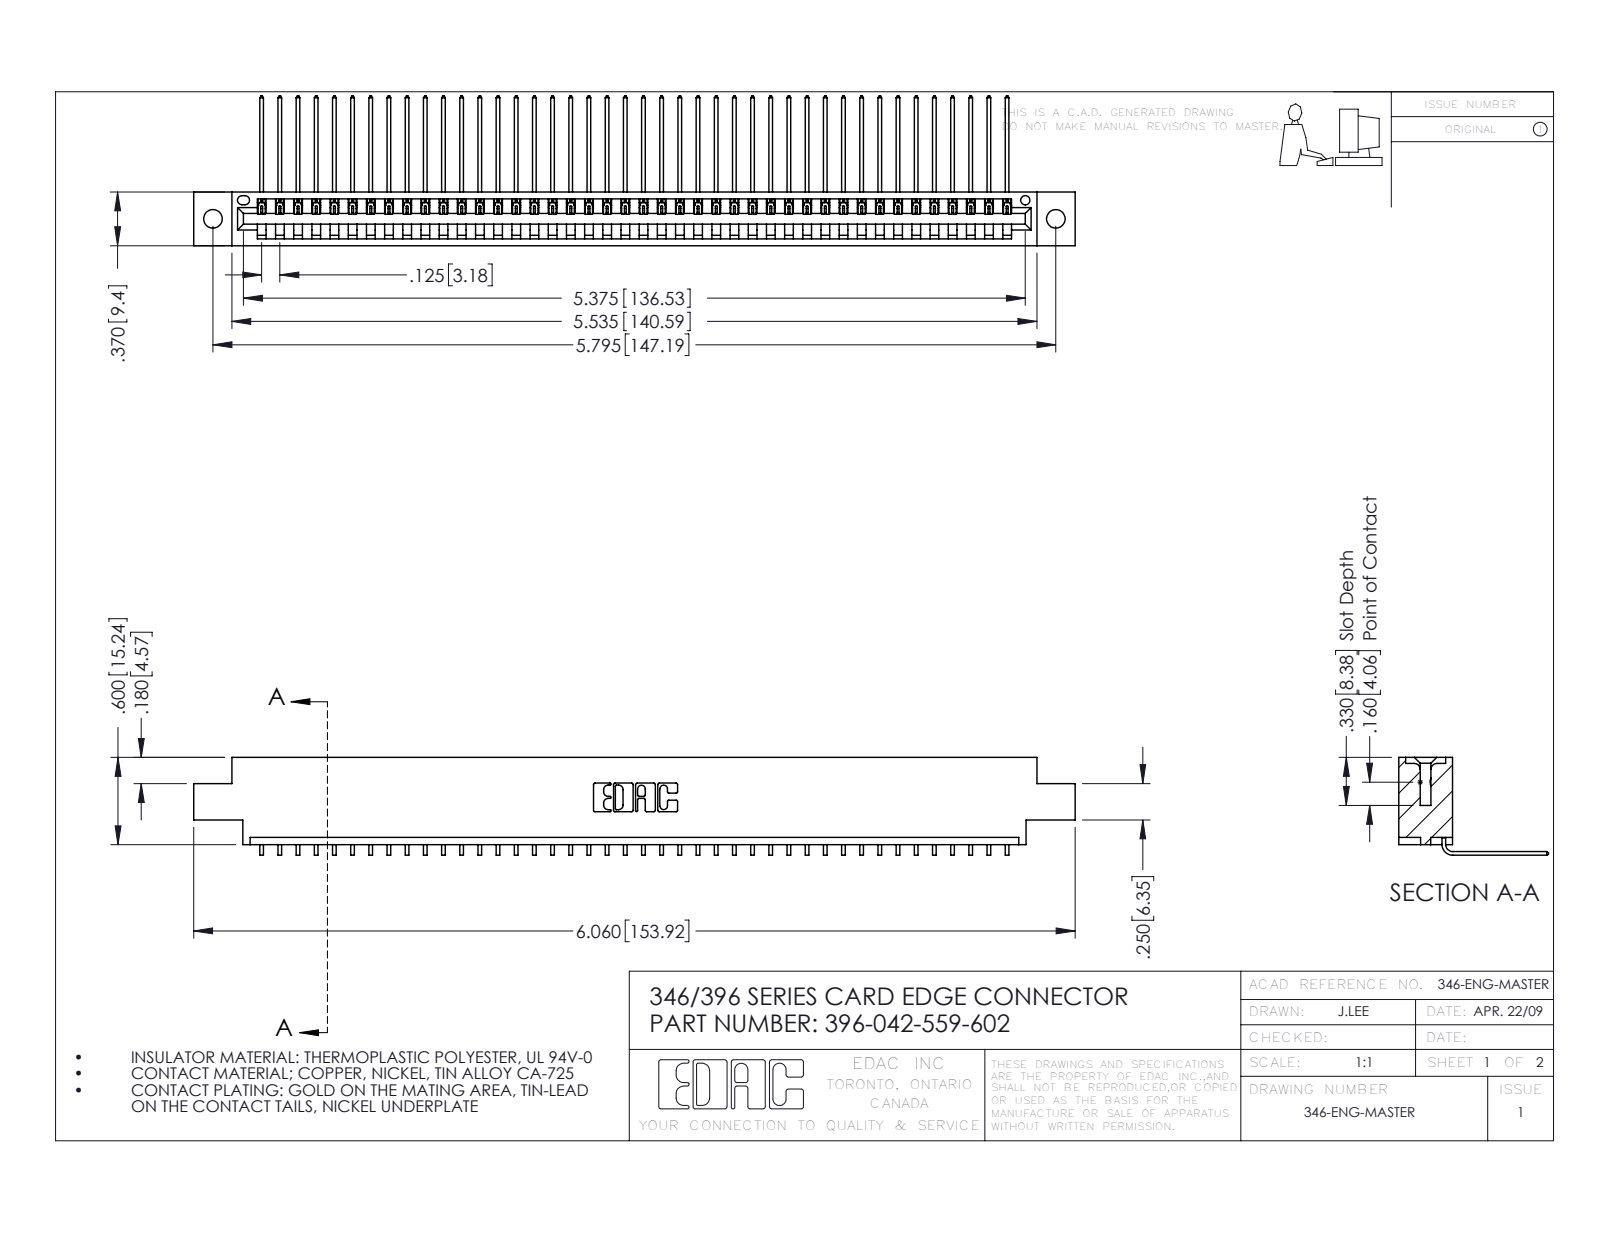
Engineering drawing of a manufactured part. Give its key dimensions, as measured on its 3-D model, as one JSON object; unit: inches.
{"part_name": "345-292-001_558 559 Tail - 1; 346 Part_0.170 Offset - 0.128 Dia; 396-042-559-602", "step_written_by": "SolidWorks 2016 (CONFIG_CONTROL_DESIGN)", "units": "inches", "bodies": {"solids": 43, "faces": 2646, "planar": 1844, "cylindrical": 802, "other": 0}, "overall_size": [6.06, 1.03, 0.673], "volume_in3": 0.896, "surface_area_in2": 29.57, "round_holes": [[0.128, 2], [0.064, 1]], "partial_cylinders_radius": [[0.006, 84], [0.01, 22], [0.007, 6], [0.031, 6], [0.026, 3], [0.031, 2], [0.04, 2], [0.014, 1]], "face_to_face_distances": [0.048, 0.322, 0.37, 0.25, 0.025, 0.072, 0.298, 0.148, 0.222, 0.1], "hole_center_spacings": [0.246, 5.586, 5.795]}
